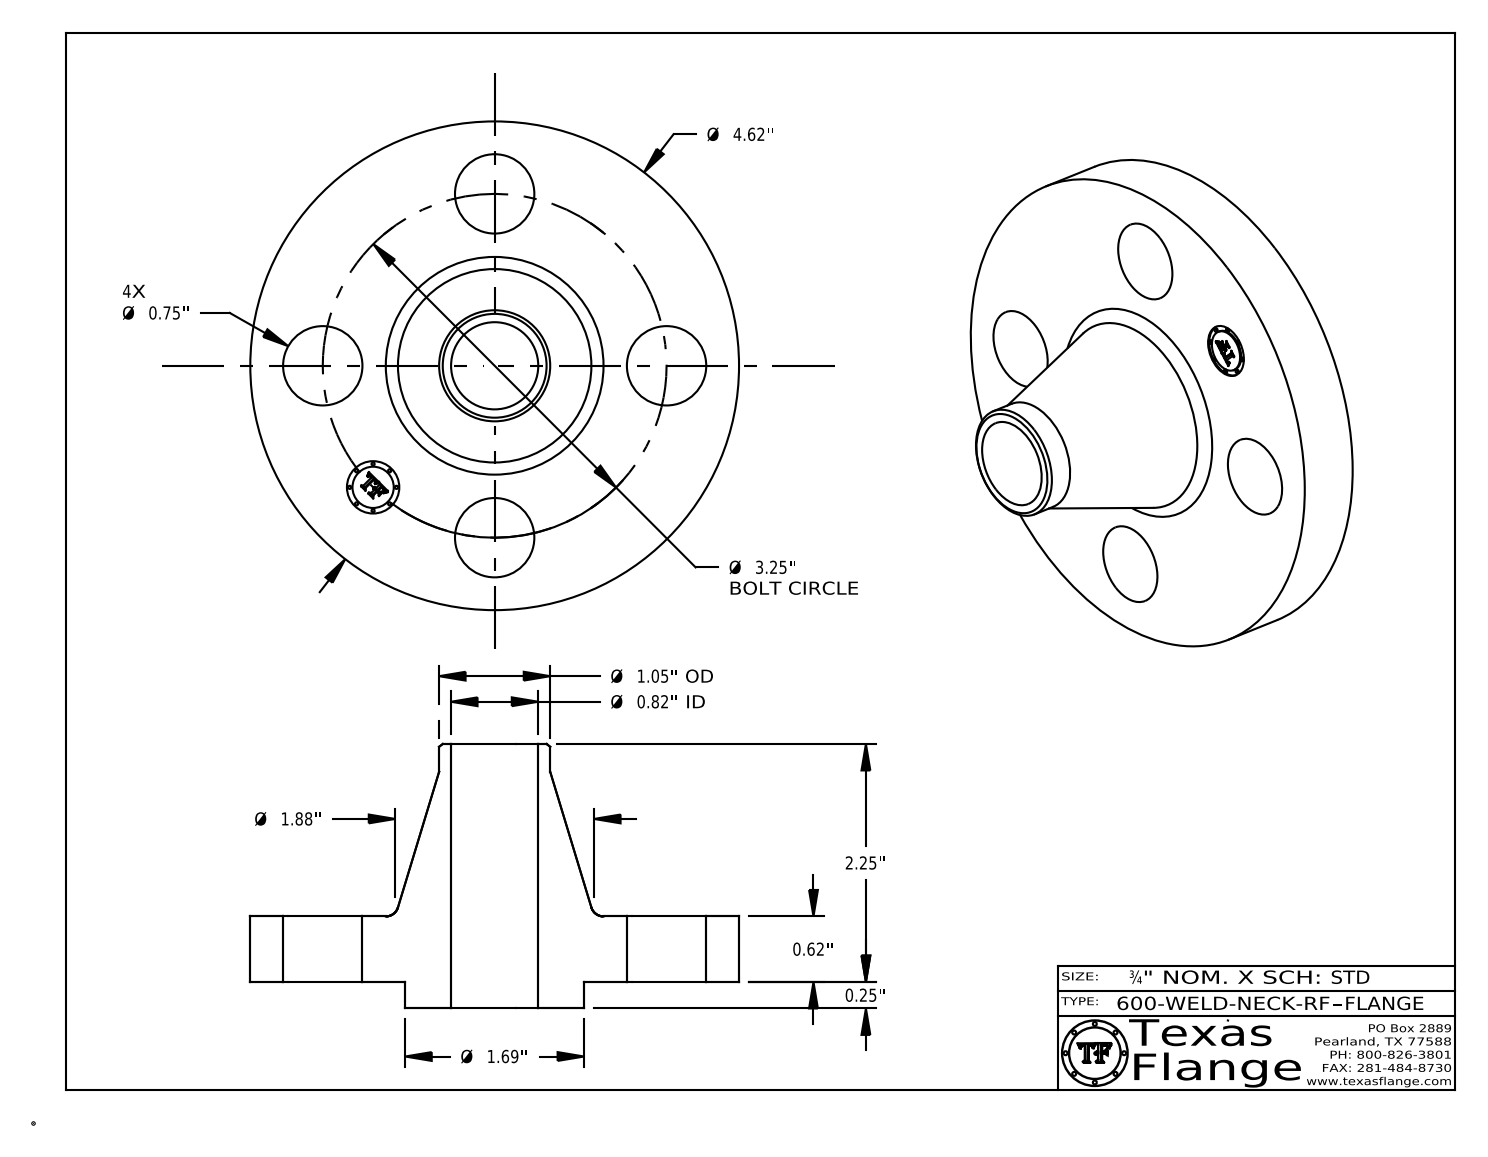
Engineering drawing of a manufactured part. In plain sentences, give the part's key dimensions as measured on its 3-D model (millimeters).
The part is named "600-WELD-NECK-RF". Its 3-D file was written by "CATIA V5 STEP AP214 (AUTOMOTIVE_DESIGN)". It is 1 solid with 411 faces: 369 planar, 36 cylindrical and 6 other. Overall it measures 117.3 by 117.3 by 63.5 millimeters. Its volume is 182 400 cubic millimeters and its surface area 36 770 square millimeters. Round holes: 4 of diameter 19.1, 1 of diameter 12.6, 1 of diameter 20.9. Round bosses or shafts: 8 of diameter 0.8, 1 of diameter 117.3, 1 of diameter 42.9, 1 of diameter 26.7, 1 of diameter 9.9. The main face-to-face distances are 15.7, 6.4, 22.1, 63.5, 57.2, 41.4, 21.7, 15.4, 0.4, 41.8. The hole center spacings are 41.3, 58.4, 31.6, 76.3, 82.6.
